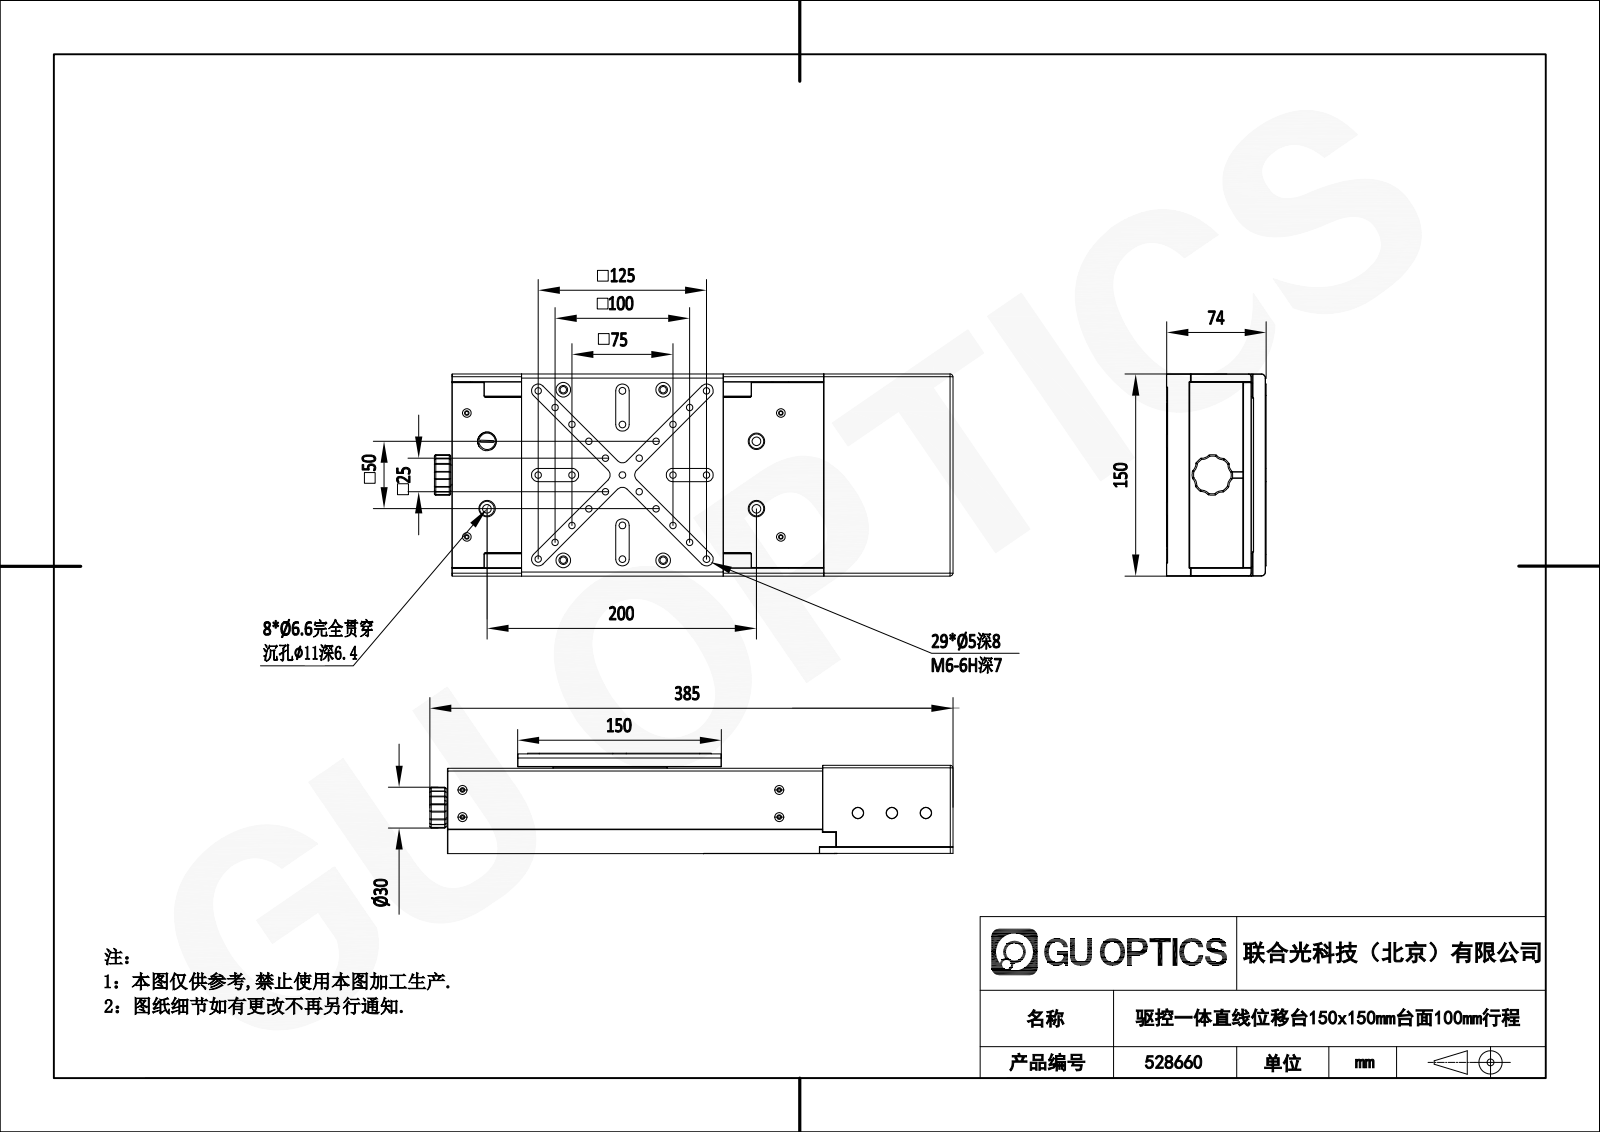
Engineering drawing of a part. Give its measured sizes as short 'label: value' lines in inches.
name: 528660
written by: SolidWorks 2020 (CONFIG_CONTROL_DESIGN)
unit: in
bodies: 45 solids, 2748 faces (1471 planar, 794 cylindrical, 483 other)
size: 15.157 × 5.906 × 2.913
volume: 161.5 in³; area: 940.9 in²
holes: 42× ⌀0.197, 27× ⌀0.098, 27× ⌀0.134, 19× ⌀0.256, 16× ⌀0.138, 14× ⌀0.26, 14× ⌀0.433, 12× ⌀0.236, 9× ⌀0.13, 8× ⌀0.097, 8× ⌀0.097, 8× ⌀0.492
bosses: 1× ⌀1.504, 1× ⌀0.945, 1× ⌀0.748, 1× ⌀0.63, 1× ⌀0.551, 1× ⌀0.416, 1× ⌀0.118
rounds: 34× R0.039, 20× R0.197, 13× R0.079, 8× R0.295, 6× R0.059, 5× R0.157, 2× R0.012, 2× R0.03
face distances: 0.236, 0.039, 2.224, 0.689, 1.535, 2.461, 0.65, 2.185, 1.772, 0.354
hole spacings: 1.575, 4.299, 1.969, 3.15, 5.091, 4, 4.724, 6.19
